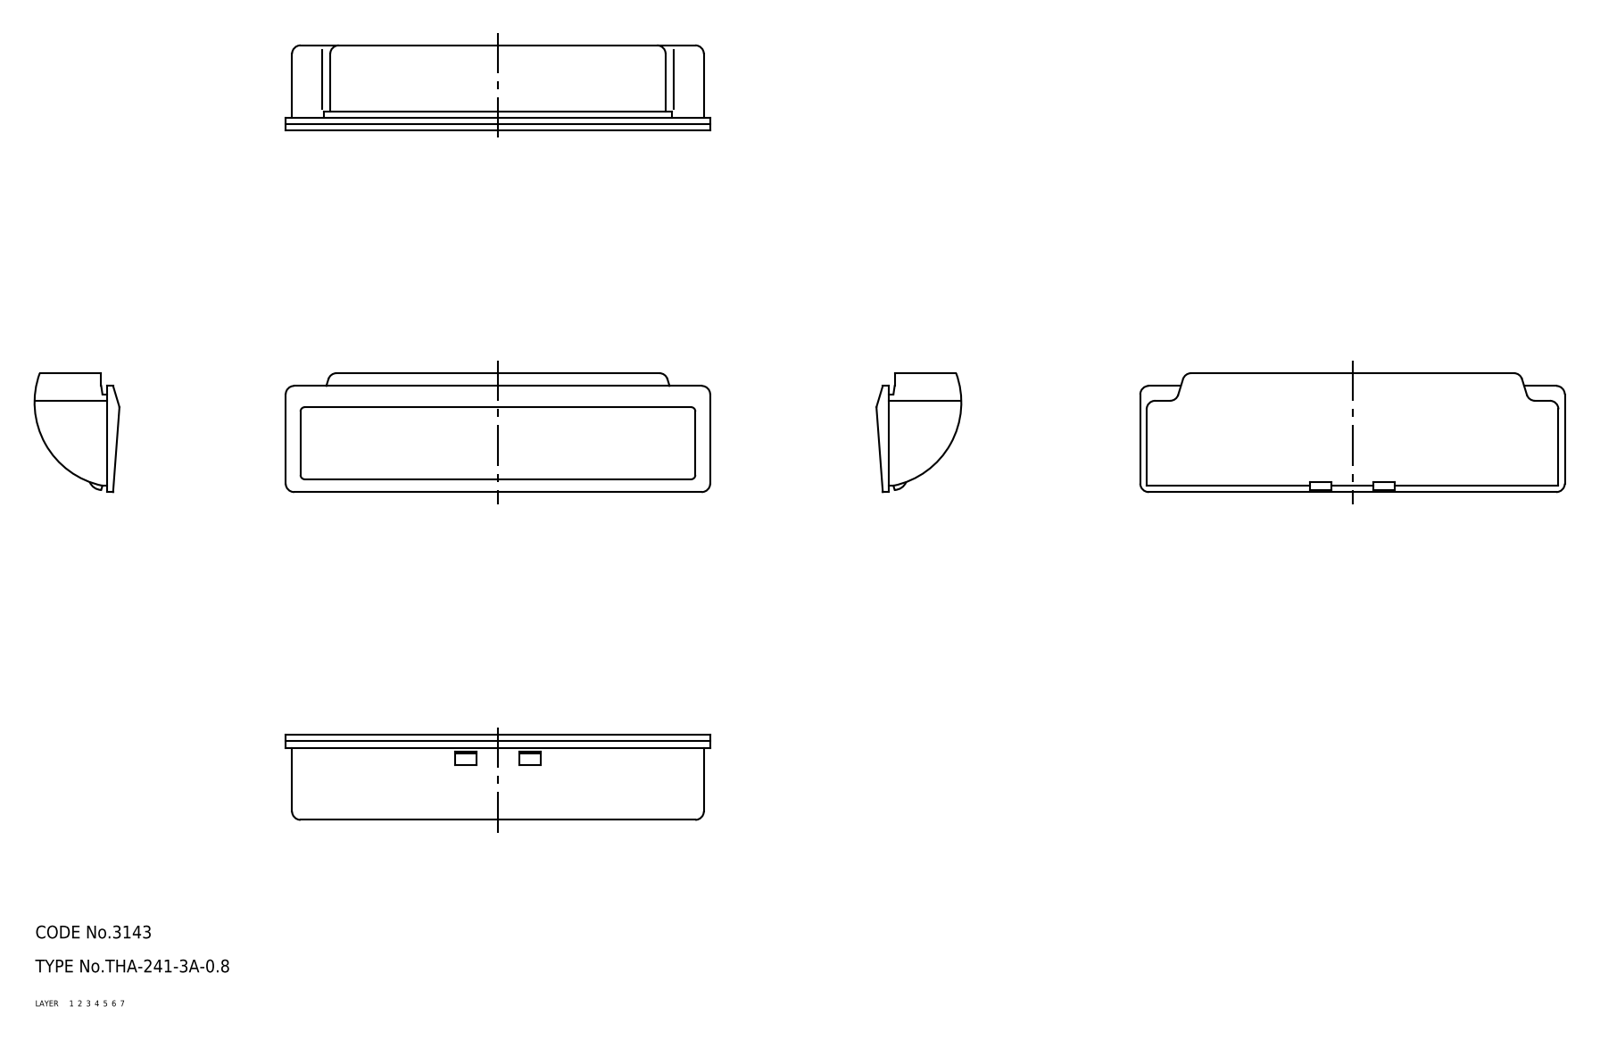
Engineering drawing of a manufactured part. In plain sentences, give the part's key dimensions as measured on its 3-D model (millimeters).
The part is named "pull". Its 3-D file was written by "CADfix (AUTOMOTIVE_DESIGN)". It is 1 solid with 77 faces: 0 planar, 0 cylindrical and 77 other. Overall it measures 100 by 28 by 20 millimeters. Its volume is 11 717 cubic millimeters and its surface area 13 143 square millimeters.
